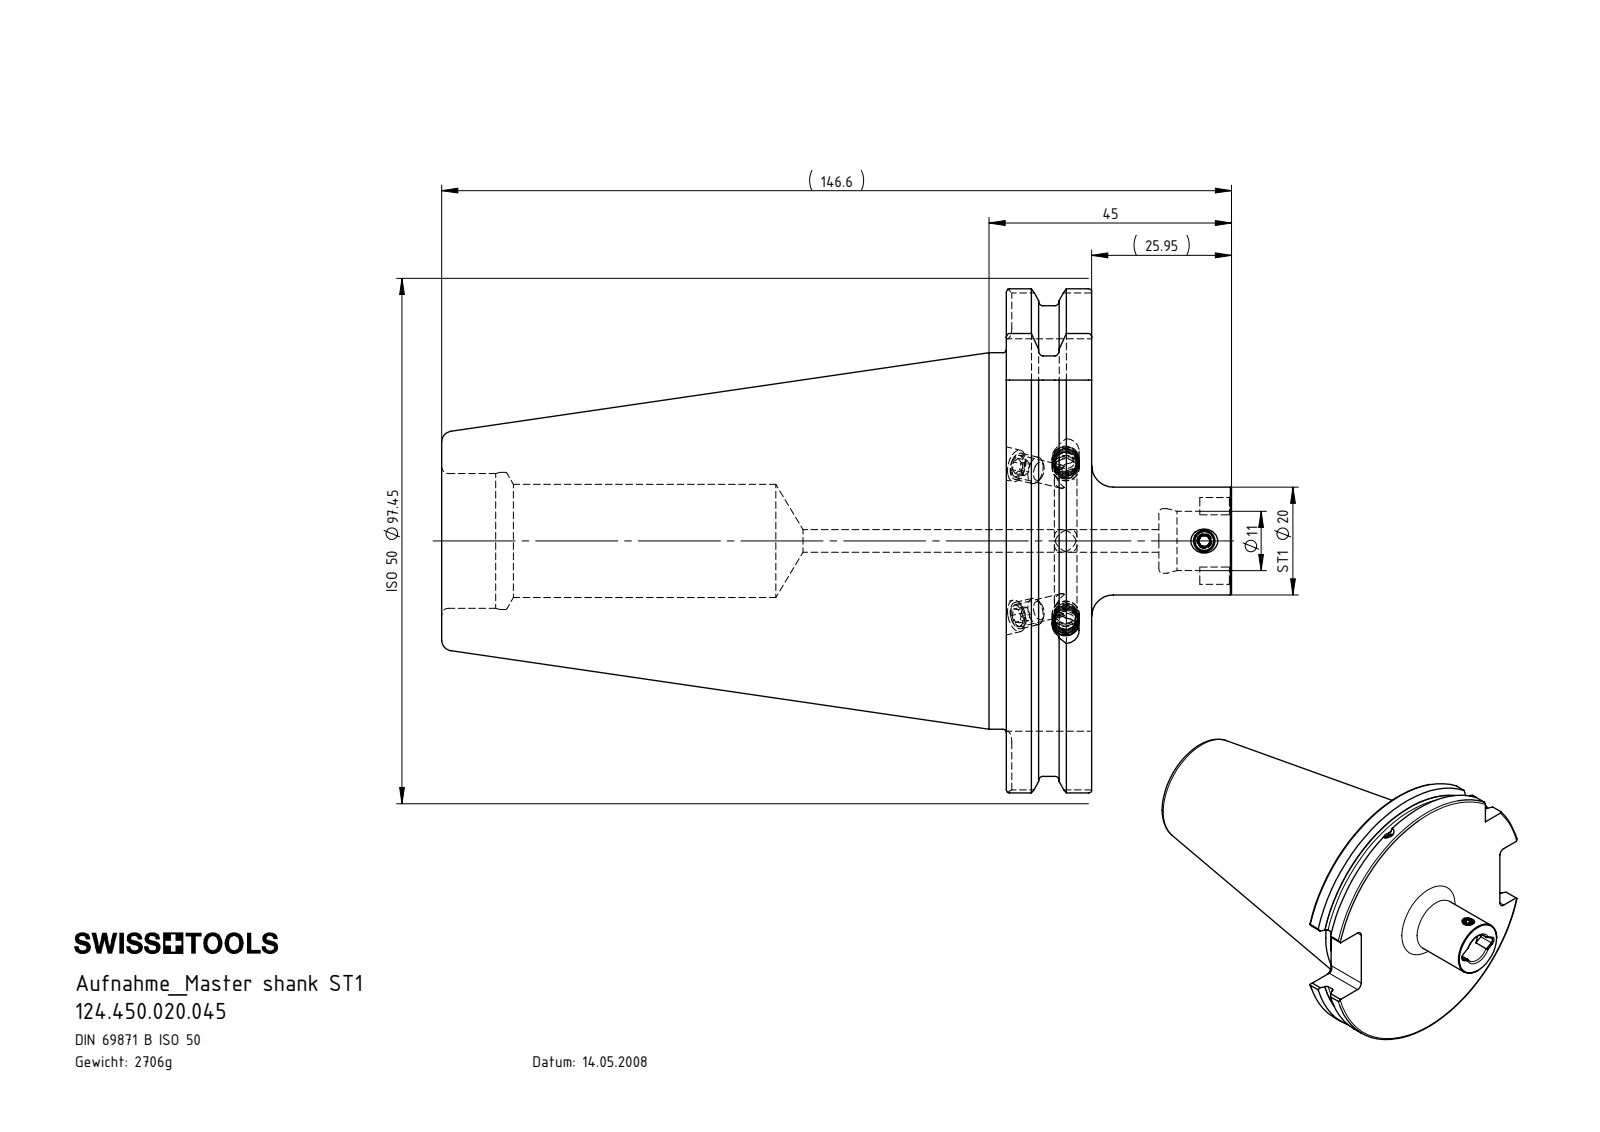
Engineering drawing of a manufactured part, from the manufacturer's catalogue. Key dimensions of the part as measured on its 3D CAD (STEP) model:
Part name (STEP PRODUCT): KVT_MB_600_050; SB5-ST1.K01.045_C_mit Bundkhlung; ST1-ER1.001.005_A; SB5.ST1.K01.045 (+1 more)
STEP written by: SolidWorks 2017 (AUTOMOTIVE_DESIGN)
Units: millimetres
Bodies: 8 solids, 207 faces (78 planar, 47 cylindrical, 82 other)
Overall size (bounding box): 146.6 × 97.45 × 93.51
Volume: 344 684 mm³ · Surface area: 44 828 mm²
Round holes (diameter × count): ⌀4.2 ×4, ⌀4 ×2, ⌀6 ×2, ⌀2 ×1, ⌀3.5 ×1, ⌀5 ×1, ⌀11 ×1, ⌀12 ×1, ⌀21 ×1, ⌀25 ×1, ⌀25.45 ×1
Round bosses / shafts (diameter × count): ⌀5 ×3, ⌀91 ×1, ⌀69.85 ×1, ⌀20 ×1, ⌀4 ×1
Partial cylindrical surfaces — rounded edges, fillets, slot ends (radius × count): R2 ×8, R1.3 ×2, R48.73 ×1
Main face-to-face distances: 15.85, 104.8, 120.65, 72.8, 25.7, 146.6, 41.8, 25.95, 42.7, 17
